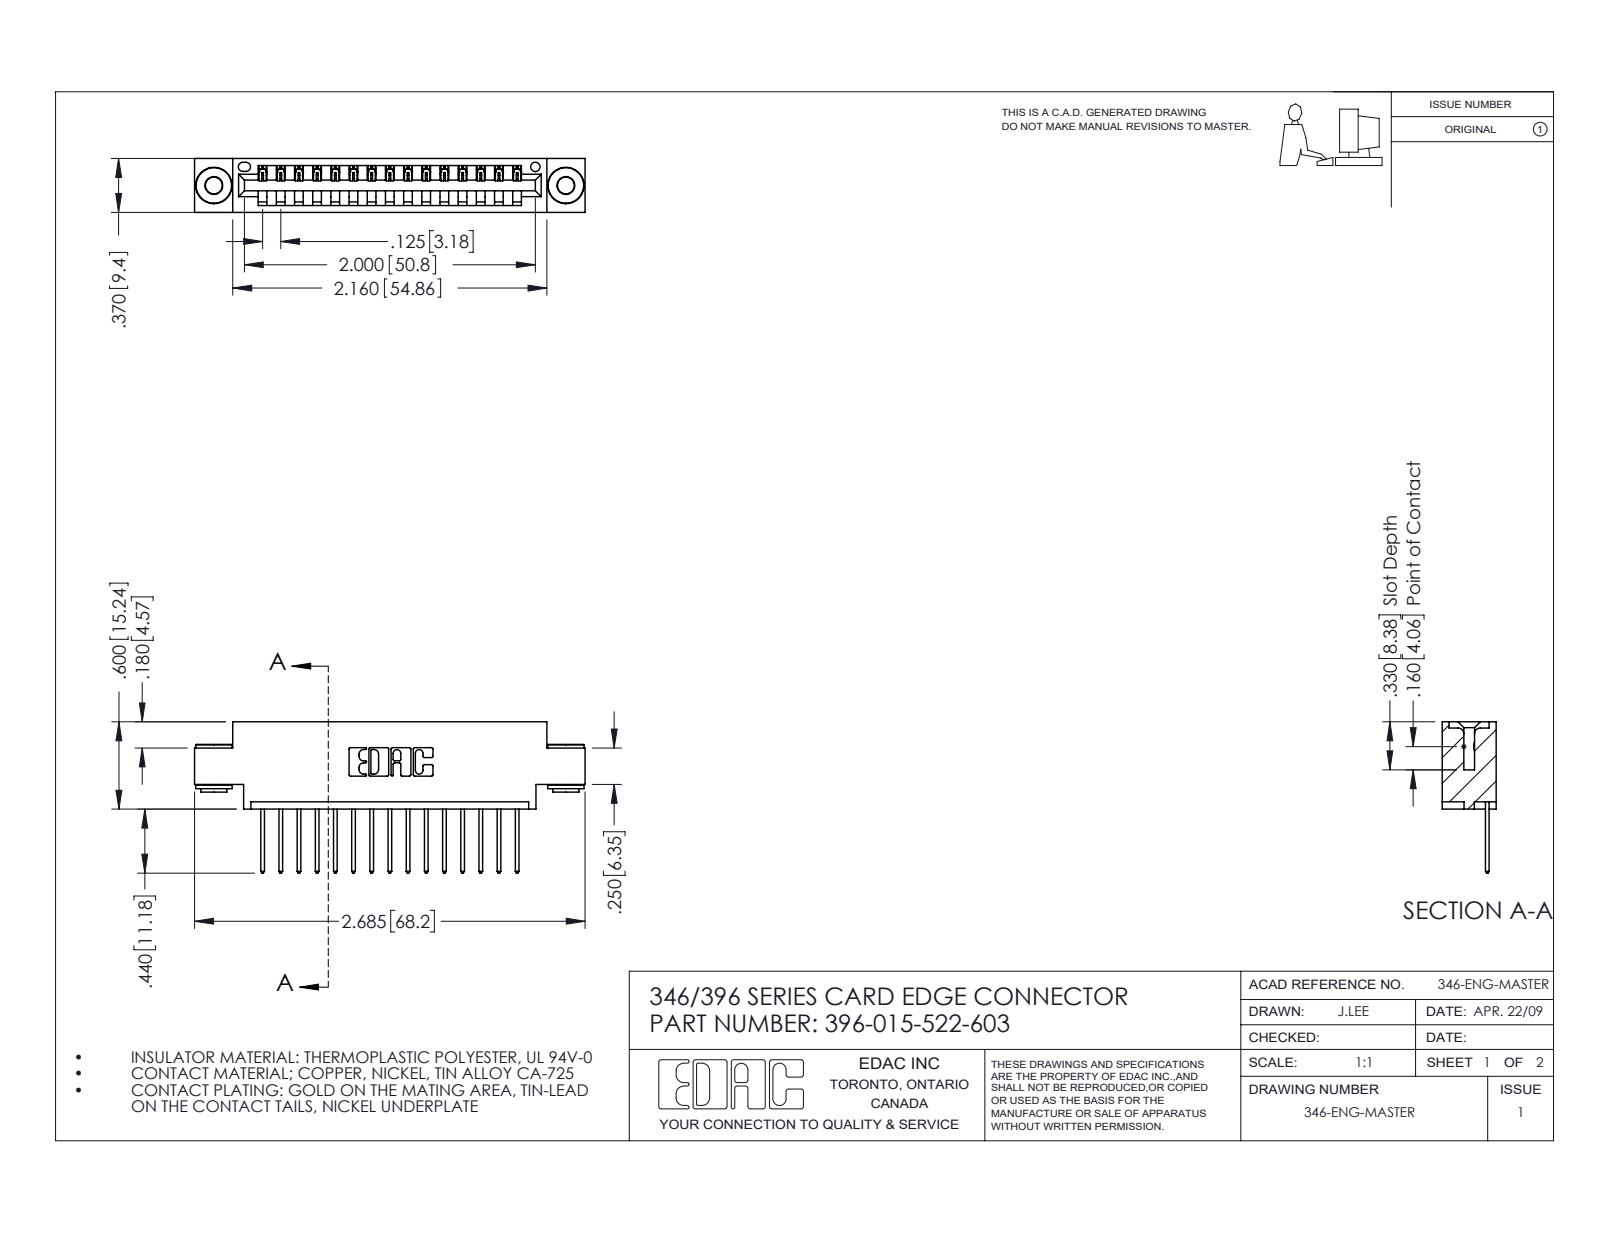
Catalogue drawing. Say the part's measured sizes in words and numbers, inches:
The part is named "346 Part_0.170 Offset - 0.156 Dia-TH; 396-015-522-603; 345-250-002_345-250-002-102; 345-292-001_345-293-122". Its 3-D file was written by "SolidWorks 2016 (CONFIG_CONTROL_DESIGN)". It is 18 solids with 1034 faces: 690 planar, 336 cylindrical and 8 other. Overall it measures 2.685 by 1.04 by 0.37 inches. Its volume is 0.379 cubic inches and its surface area 12.25 square inches. Round holes: 2 of diameter 0.116, 2 of diameter 0.156, 1 of diameter 0.064. Round bosses or shafts: 2 of diameter 0.25, 2 of diameter 0.18, 2 of diameter 0.136. Partial cylindrical surfaces (rounded edges, fillets, slot ends): 30 of radius 0.006, 30 of radius 0.01, 22 of radius 0.01, 6 of radius 0.007, 6 of radius 0.031, 3 of radius 0.026, 2 of radius 0.031, 2 of radius 0.04. The main face-to-face distances are 0.37, 0.048, 0.322, 0.25, 0.025, 0.072, 0.298, 0.148, 0.222, 0.1. The hole center spacings are 0.246, 2.213, 2.42.
